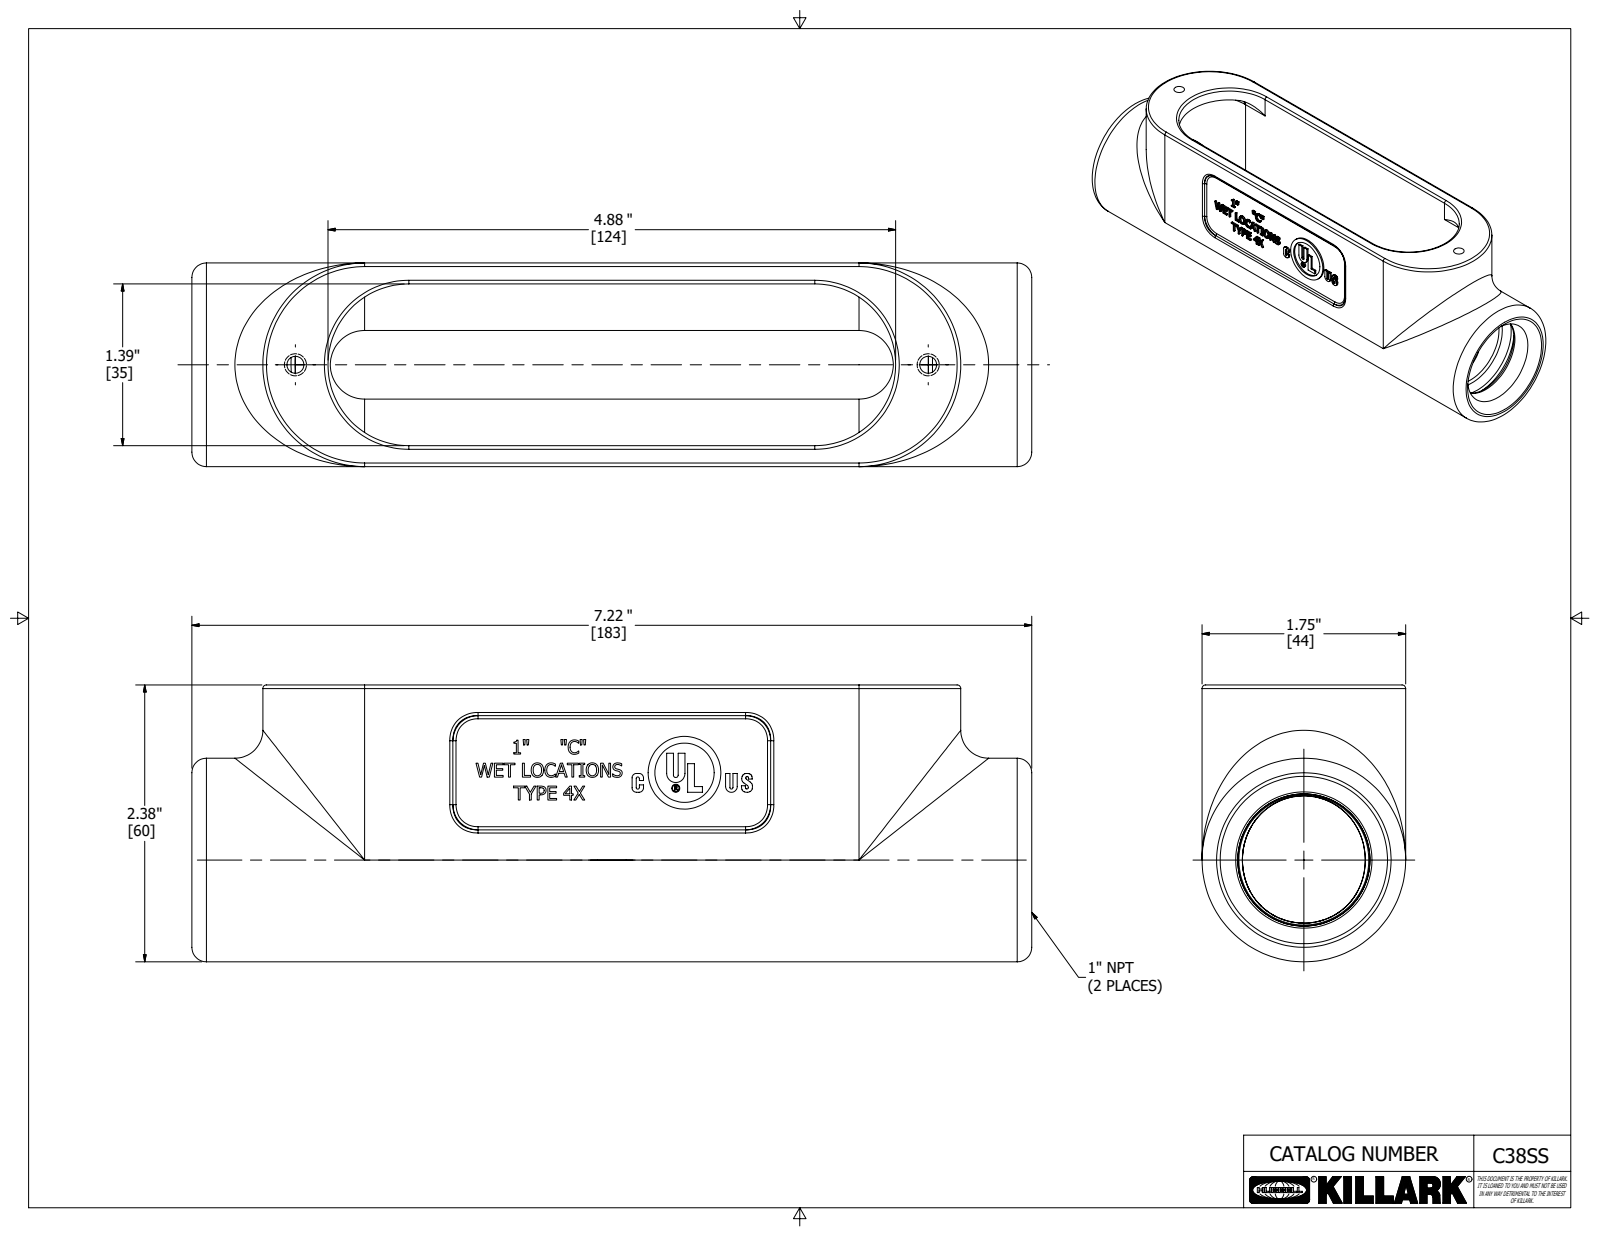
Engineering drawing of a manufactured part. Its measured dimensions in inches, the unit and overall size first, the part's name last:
Units: inches
Overall size (bounding box): 7.22 × 2.38 × 1.75
Round holes (diameter × count): ⌀0.145 ×2, ⌀0.058 ×1, ⌀0.509 ×1, ⌀1.321 ×1
Round bosses / shafts (diameter × count): ⌀1.75 ×1, ⌀0.625 ×1, ⌀0.069 ×1
Partial cylindrical surfaces — rounded edges, fillets, slot ends (radius × count): R0.031 ×13, R0.038 ×4, R0.25 ×4, R0.695 ×4, R0.013 ×2, R0.013 ×2, R0.125 ×2, R0.4 ×2
Main face-to-face distances: 1.39, 0.18, 1.57, 0.18, 1.57, 1.75, 2.2, 0.031, 0.149, 1.539
Hole centre spacings: 0.153, 5.44
Volume: 7.55 in³ · Surface area: 87.33 in²
Bodies: 1 solid, 492 faces (287 planar, 78 cylindrical, 127 other)
Part name (STEP PRODUCT): C38SS
STEP written by: Autodesk Inventor 2020 (AUTOMOTIVE_DESIGN)
